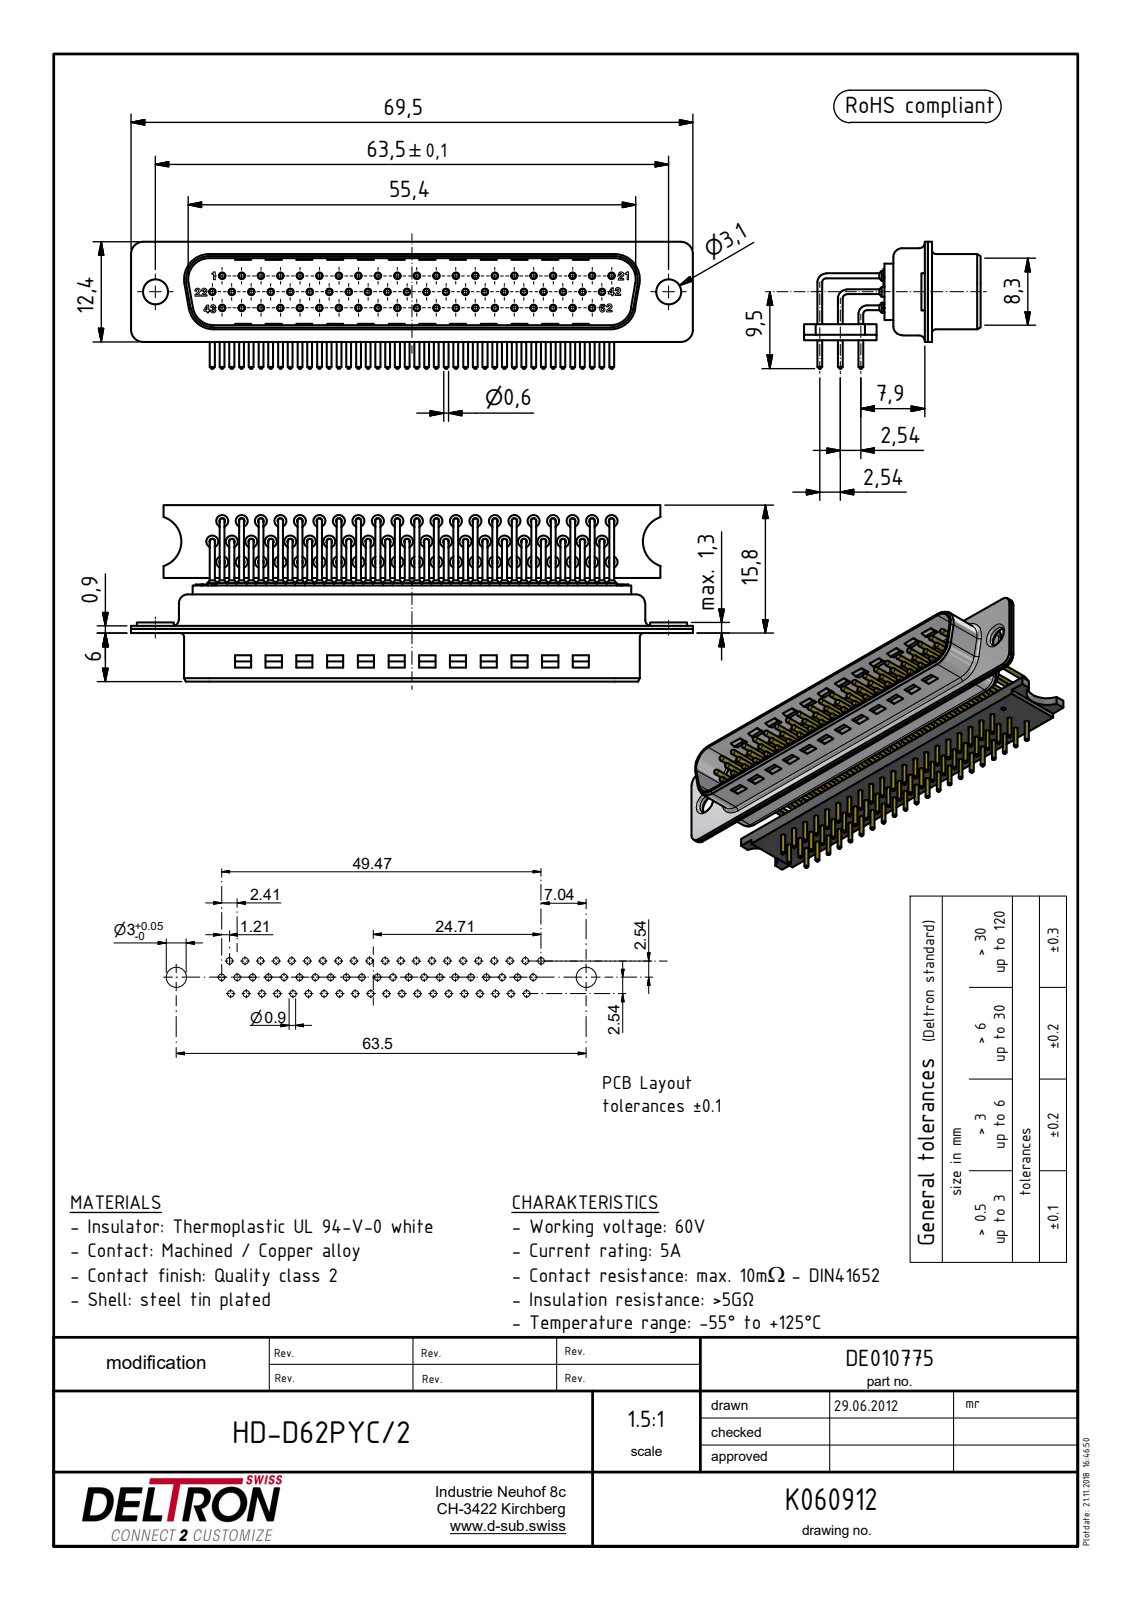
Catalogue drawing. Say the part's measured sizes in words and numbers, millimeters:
The part is named "N00784_China_BG; R+B00744_BG; R+B00745_BG; R+B00746_BG (+4 more)". Its 3-D file was written by "Autodesk Inventor 2015 (AUTOMOTIVE_DESIGN)". It is 66 solids with 1763 faces: 737 planar, 639 cylindrical and 387 other. Overall it measures 69.5 by 21.84 by 15.7 millimeters. Its volume is 4 903 cubic millimeters and its surface area 12 712 square millimeters. Round holes: 63 of diameter 0.7, 62 of diameter 0.8, 62 of diameter 1.26, 62 of diameter 1.6, 2 of diameter 3.1, 2 of diameter 4.06. Round bosses or shafts: 124 of diameter 0.6, 62 of diameter 1.24, 62 of diameter 0.75, 2 of diameter 4.6, 2 of diameter 3.9. Partial cylindrical surfaces (rounded edges, fillets, slot ends): 8 of radius 0.7, 8 of radius 1.1, 8 of radius 1.5, 8 of radius 2, 6 of radius 1.3, 4 of radius 0.25, 4 of radius 0.5, 4 of radius 1. The main face-to-face distances are 0.5, 2, 0.4, 0.75, 9.55, 8.8, 1.5, 8.15, 0.65, 1.1. The hole center spacings are 2.41, 4.82, 7.23, 9.64, 2.81, 12.05, 14.46, 16.87.
